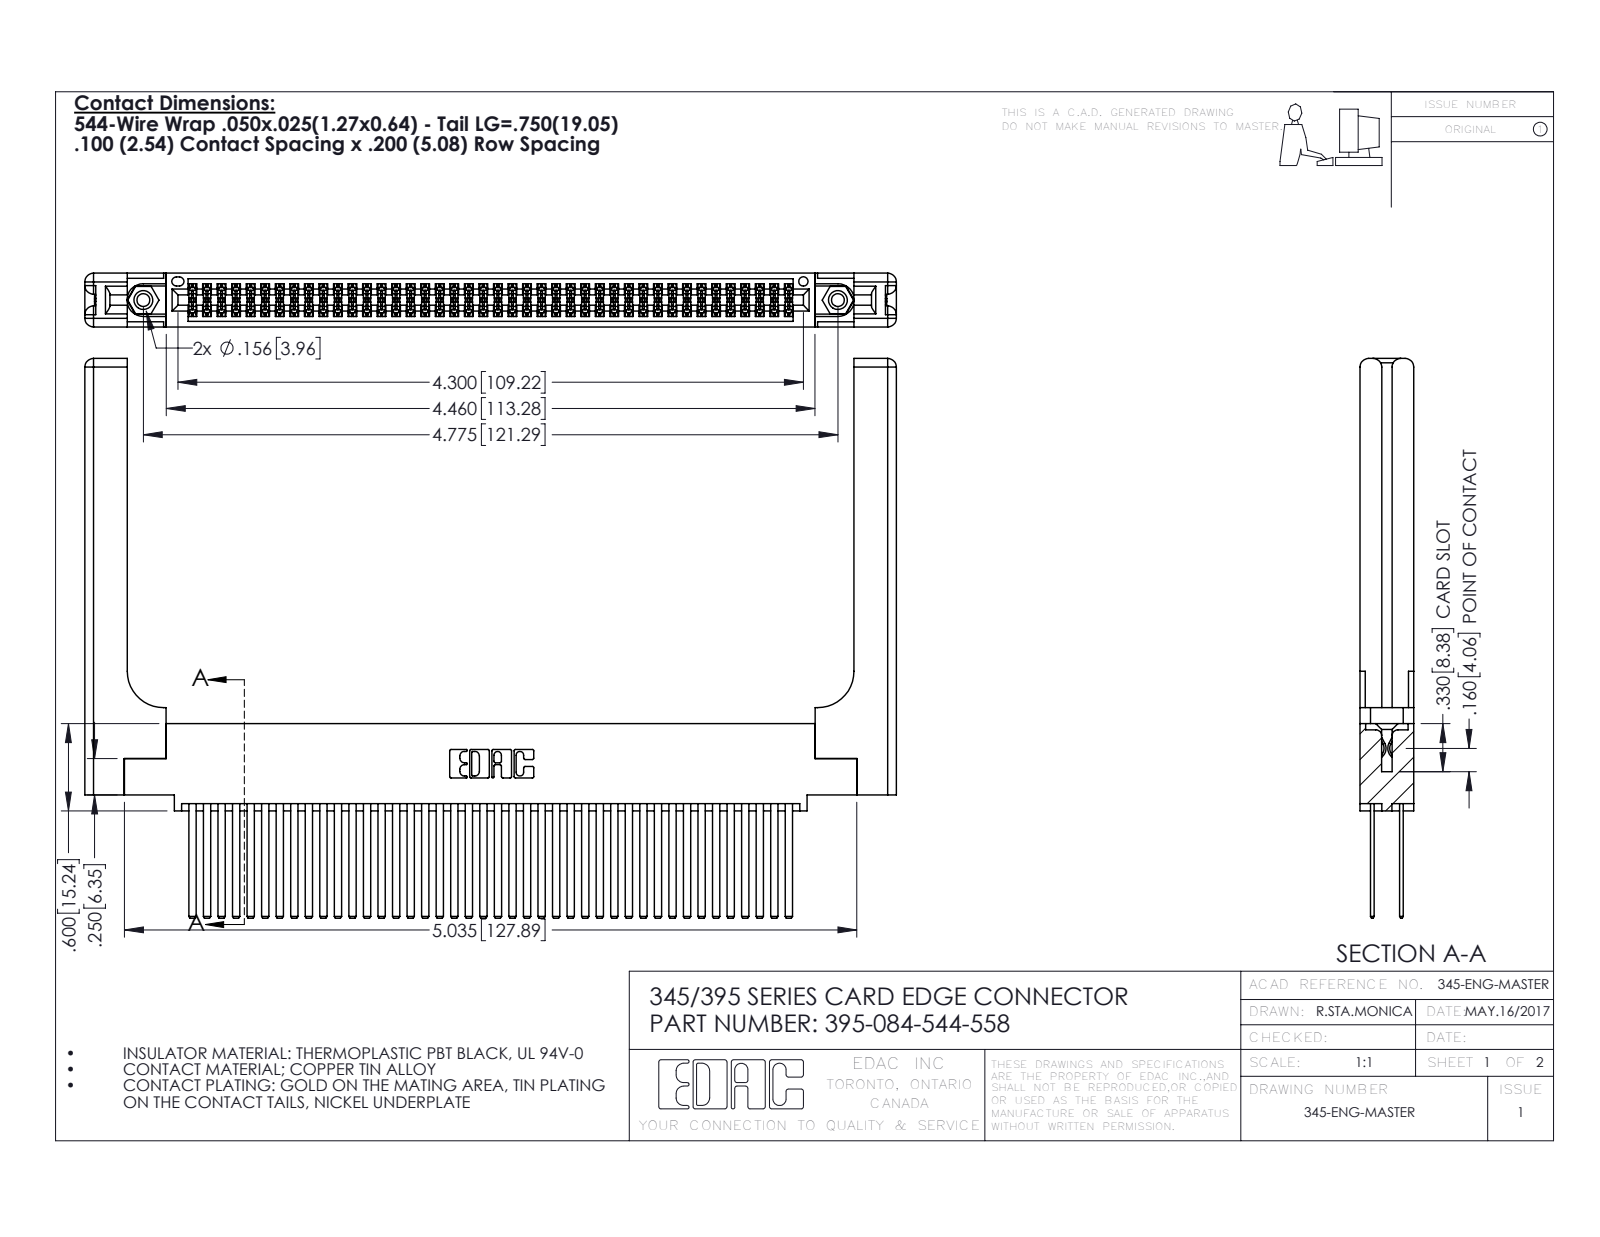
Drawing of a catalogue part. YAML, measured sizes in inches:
part_name: "345-292-001_345-293-144; 345-220-058_345-220-058; 395-084-544-558; 345-250-001_345-250-001-102 (+1 more)"
step_written_by: "SolidWorks 2016 (CONFIG_CONTROL_DESIGN)"
units: inches
bodies: {solids: 89, faces: 4082, planar: 2668, cylindrical: 1354, other: 60}
overall_size: [5.579, 3.847, 0.37]
volume: 1.425
surface_area: 47.4
round_holes:
  - {diameter: 0.089, count: 2}
  - {diameter: 0.125, count: 2}
  - {diameter: 0.156, count: 2}
  - {diameter: 0.064, count: 1}
round_bosses_or_shafts:
  - {diameter: 0.155, count: 2}
partial_cylinders:
  - {radius: 0.006, count: 126}
  - {radius: 0.01, count: 22}
  - {radius: 0.06, count: 16}
  - {radius: 0.007, count: 6}
  - {radius: 0.031, count: 6}
  - {radius: 0.026, count: 3}
  - {radius: 0.014, count: 2}
  - {radius: 0.019, count: 2}
face_to_face_distances: [0.072, 0.298, 0.098, 0.272, 0.025, 0.2, 0.37, 0.225, 0.175, 0.148]
hole_center_spacings: [0.27, 4.539, 4.775]
